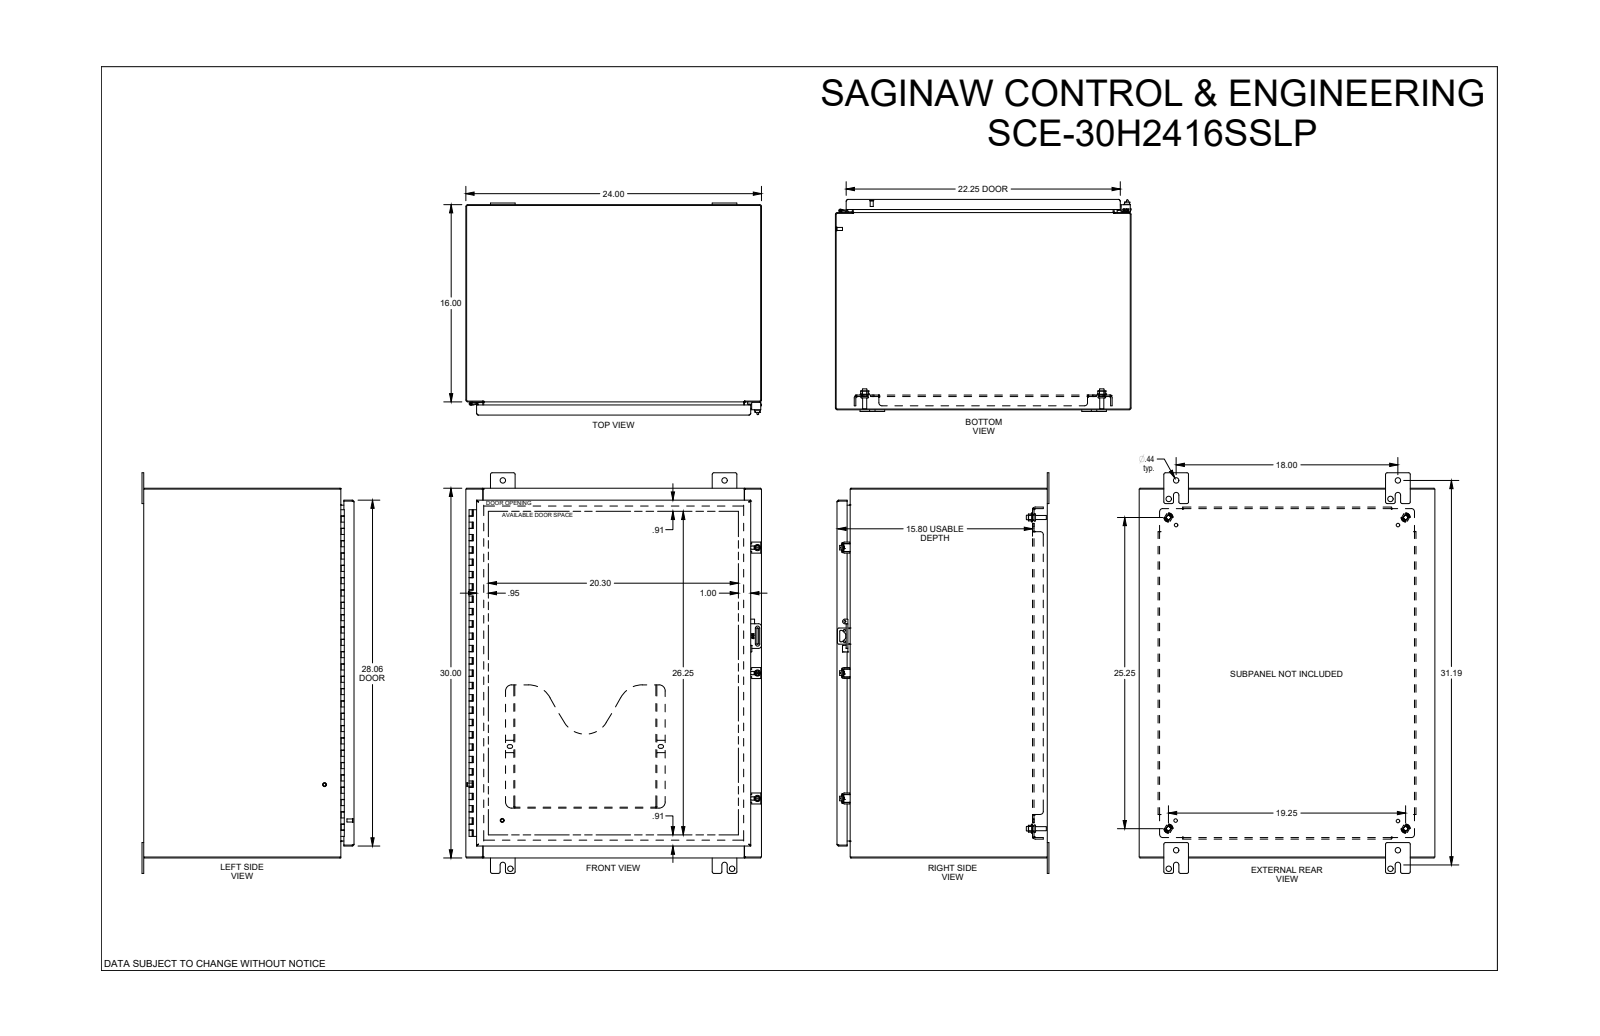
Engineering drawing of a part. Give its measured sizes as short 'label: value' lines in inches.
name: SCE-30H2416SSLP
written by: SolidWorks 2019 (CONFIG_CONTROL_DESIGN)
unit: in
bodies: 0 solids, 3825 faces (1563 planar, 800 cylindrical, 1462 other)
size: 32.5 × 24 × 17.208
holes: 8× ⌀0.437, 6× ⌀0.25, 5× ⌀0.19, 5× ⌀0.193, 5× ⌀0.203, 4× ⌀0.281, 4× ⌀0.367, 4× ⌀0.5, 2× ⌀0.16, 1× ⌀0.13, 1× ⌀0.132
bosses: 8× ⌀0.248, 6× ⌀0.563, 5× ⌀0.256, 5× ⌀0.188, 4× ⌀0.366, 4× ⌀0.332, 4× ⌀0.25, 3× ⌀0.507
rounds: 148× R0.01, 44× R0.015, 36× R0.029, 29× R0.06, 27× R0.03, 27× R0.125, 22× R0.04, 14× R0.07
face distances: 0.075, 23.925, 29.925, 16.998, 16.923, 0.075, 1.2, 15.873, 17.073, 16.998
hole spacings: 0.875, 18, 0.515, 12.75, 18.641, 0.723, 1.439, 1.619
